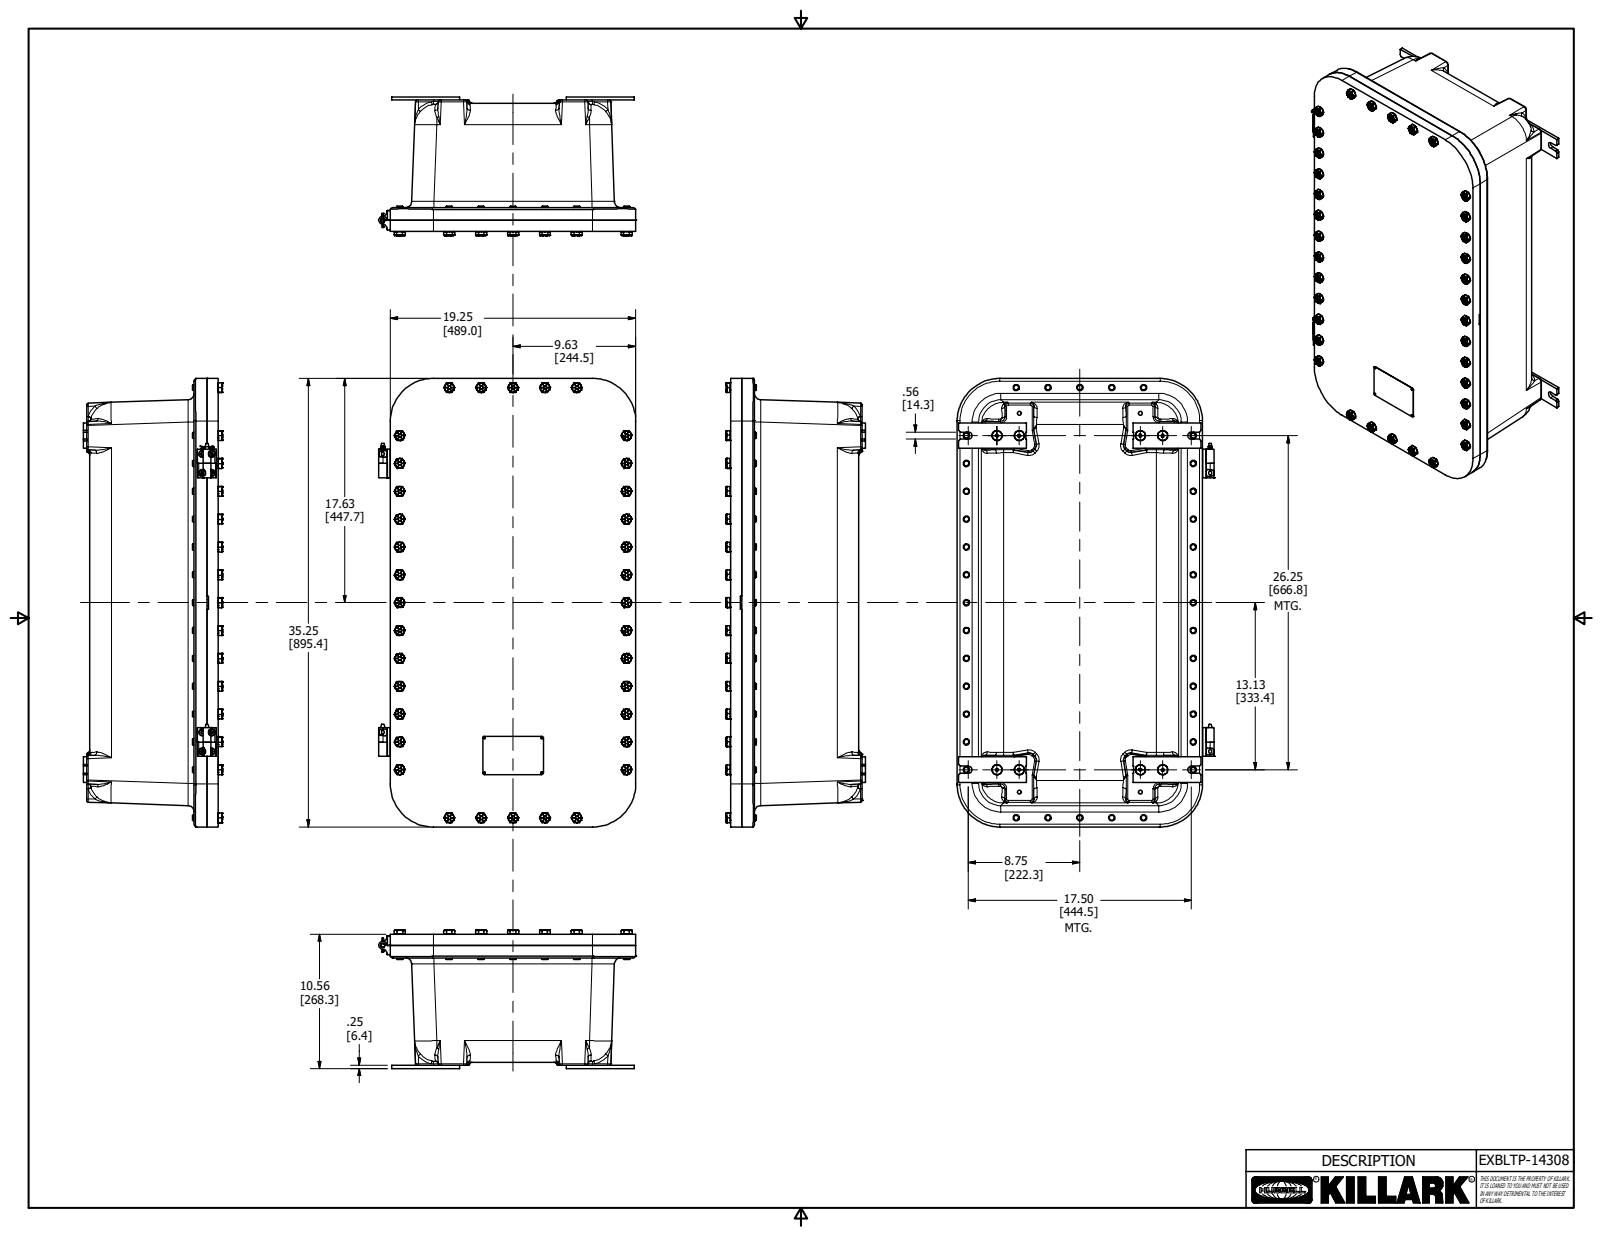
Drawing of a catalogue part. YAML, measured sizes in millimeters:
part_name: "EXBLTP - 14308 N4; 51302ABAM (EXBLT-14308); 51308AAAM; 20859AAAB (+8 more)"
step_written_by: "Autodesk Inventor 2020 (AUTOMOTIVE_DESIGN)"
units: millimeters
bodies: {solids: 71, faces: 4103, planar: 2910, cylindrical: 455, other: 738}
overall_size: [895.4, 511.9, 276.8]
volume: 27580000
surface_area: 3097000
round_holes:
  - {diameter: 10.6, count: 36}
  - {diameter: 13.5, count: 36}
  - {diameter: 7.8, count: 18}
  - {diameter: 5.6, count: 8}
  - {diameter: 6.8, count: 8}
  - {diameter: 10.3, count: 8}
  - {diameter: 2.8, count: 5}
  - {diameter: 0.6, count: 4}
  - {diameter: 13.4, count: 4}
  - {diameter: 8.1, count: 1}
round_bosses_or_shafts:
  - {diameter: 19.1, count: 36}
  - {diameter: 12.4, count: 36}
  - {diameter: 12.4, count: 8}
  - {diameter: 9.3, count: 8}
  - {diameter: 6.2, count: 8}
  - {diameter: 2.5, count: 4}
  - {diameter: 2.1, count: 4}
  - {diameter: 15.7, count: 1}
partial_cylinders:
  - {radius: 2.3, count: 48}
  - {radius: 6.4, count: 34}
  - {radius: 3.2, count: 29}
  - {radius: 0.8, count: 16}
  - {radius: 1.1, count: 12}
  - {radius: 25.4, count: 8}
  - {radius: 44.5, count: 8}
  - {radius: 7.1, count: 4}
face_to_face_distances: [22.2, 19.1, 214.3, 19.1, 236.6, 233.3, 255.6, 25.4, 6.4, 207.9]
hole_center_spacings: [455.5, 111.2, 465.6, 481.9, 503.8, 55.6, 222.3, 166.7]
